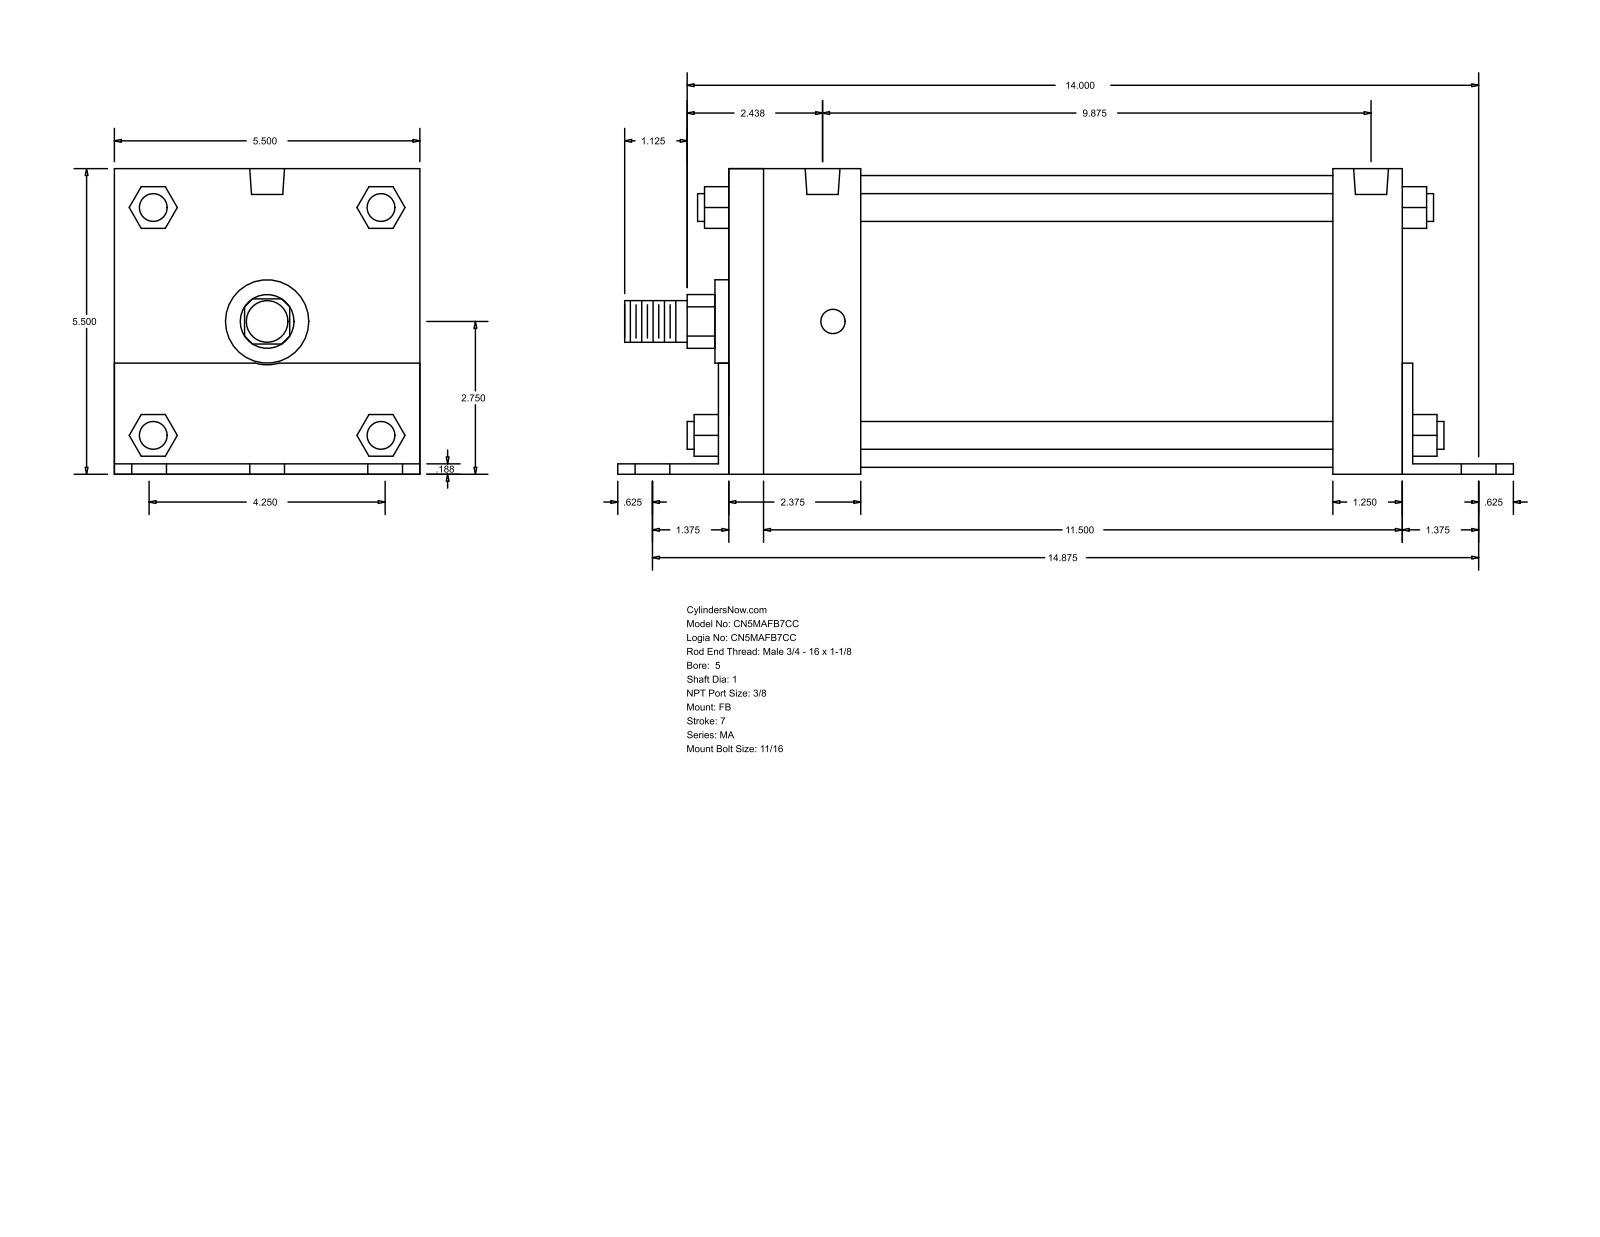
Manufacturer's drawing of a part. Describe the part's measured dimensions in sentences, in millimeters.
The part is named "MA_FB__0500_1". Its 3-D file was written by "GSSL Pune (CONFIG_CONTROL_DESIGN)". It is 0 solids with 140 faces: 105 planar, 35 cylindrical and 0 other. Overall it measures 409.57 by 139.75 by 139.7 millimeters. Round holes: 6 of diameter 17.46, 4 of diameter 11.11, 2 of diameter 15.93. Round bosses or shafts: 4 of diameter 12.7, 1 of diameter 133.35, 1 of diameter 38.1, 1 of diameter 25.4, 1 of diameter 19.05. Partial cylindrical surfaces (rounded edges, fillets, slot ends): 1 of radius 12.29, 1 of radius 19.81. The main face-to-face distances are 139.7, 4.76, 139.75, 4.71, 134.99, 307.97, 4.77, 312.74, 312.73, 317.5. The hole center spacings are 53.98, 381.67, 377.83, 4.76, 73.04, 76.33, 94.68, 98.63.
